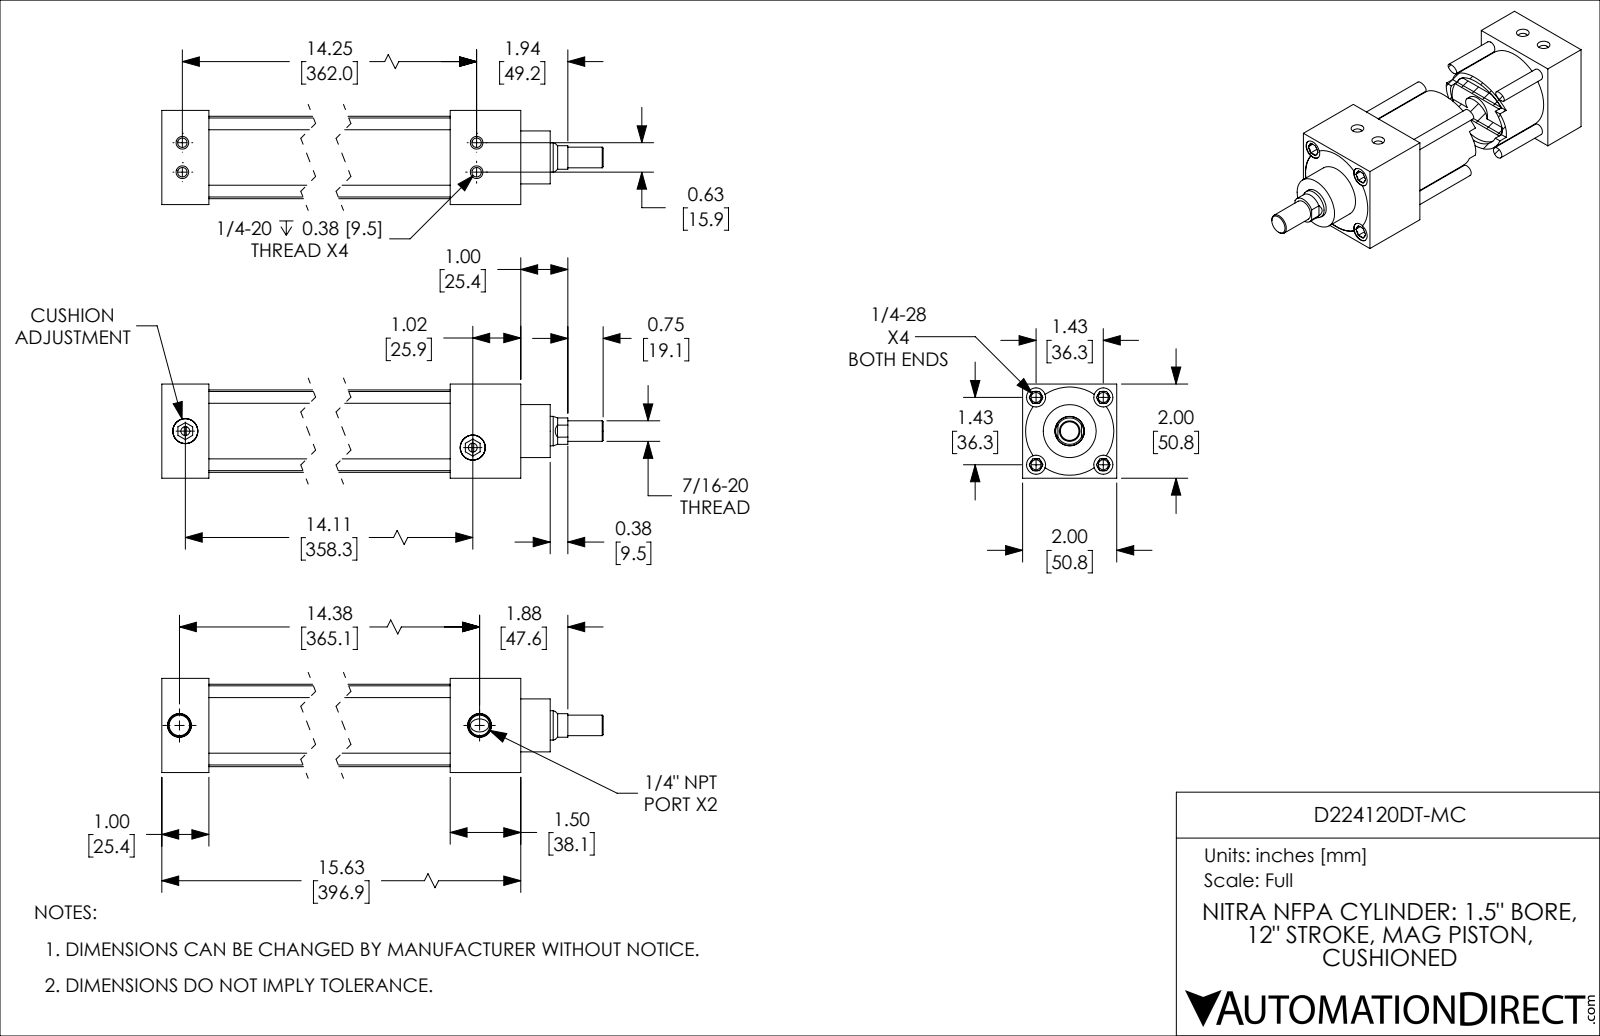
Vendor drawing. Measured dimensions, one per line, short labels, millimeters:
name: D224120DT-MC_CUSHION; D224120DT-MC_BODY; D224120DT-MC; D224120DT-MC_PISTON_KK1
written by: SolidWorks 2019 (CONFIG_CONTROL_DESIGN)
unit: mm
bodies: 4 solids, 251 faces (90 planar, 81 cylindrical, 80 other)
size: 441.3 × 50.8 × 50.8
volume: 440 200 mm³; area: 169 500 mm²
holes: 4× ⌀5.1, 4× ⌀5.4, 4× ⌀10.3, 2× ⌀4.8, 2× ⌀11.1, 2× ⌀13.5, 1× ⌀15.9, 1× ⌀38.1
bosses: 4× ⌀6.4, 2× ⌀13.5, 1× ⌀44.5, 1× ⌀38.1, 1× ⌀28.6, 1× ⌀15.8, 1× ⌀11.1
rounds: 1× R7.1, 1× R23.8
face distances: 50.8, 25.4, 358.8, 333.4, 396.7, 371.3, 38, 28.6, 54, 304.8
hole spacings: 8.1, 25.7, 36.3, 15.9, 51.4, 362, 362.3, 363.6
